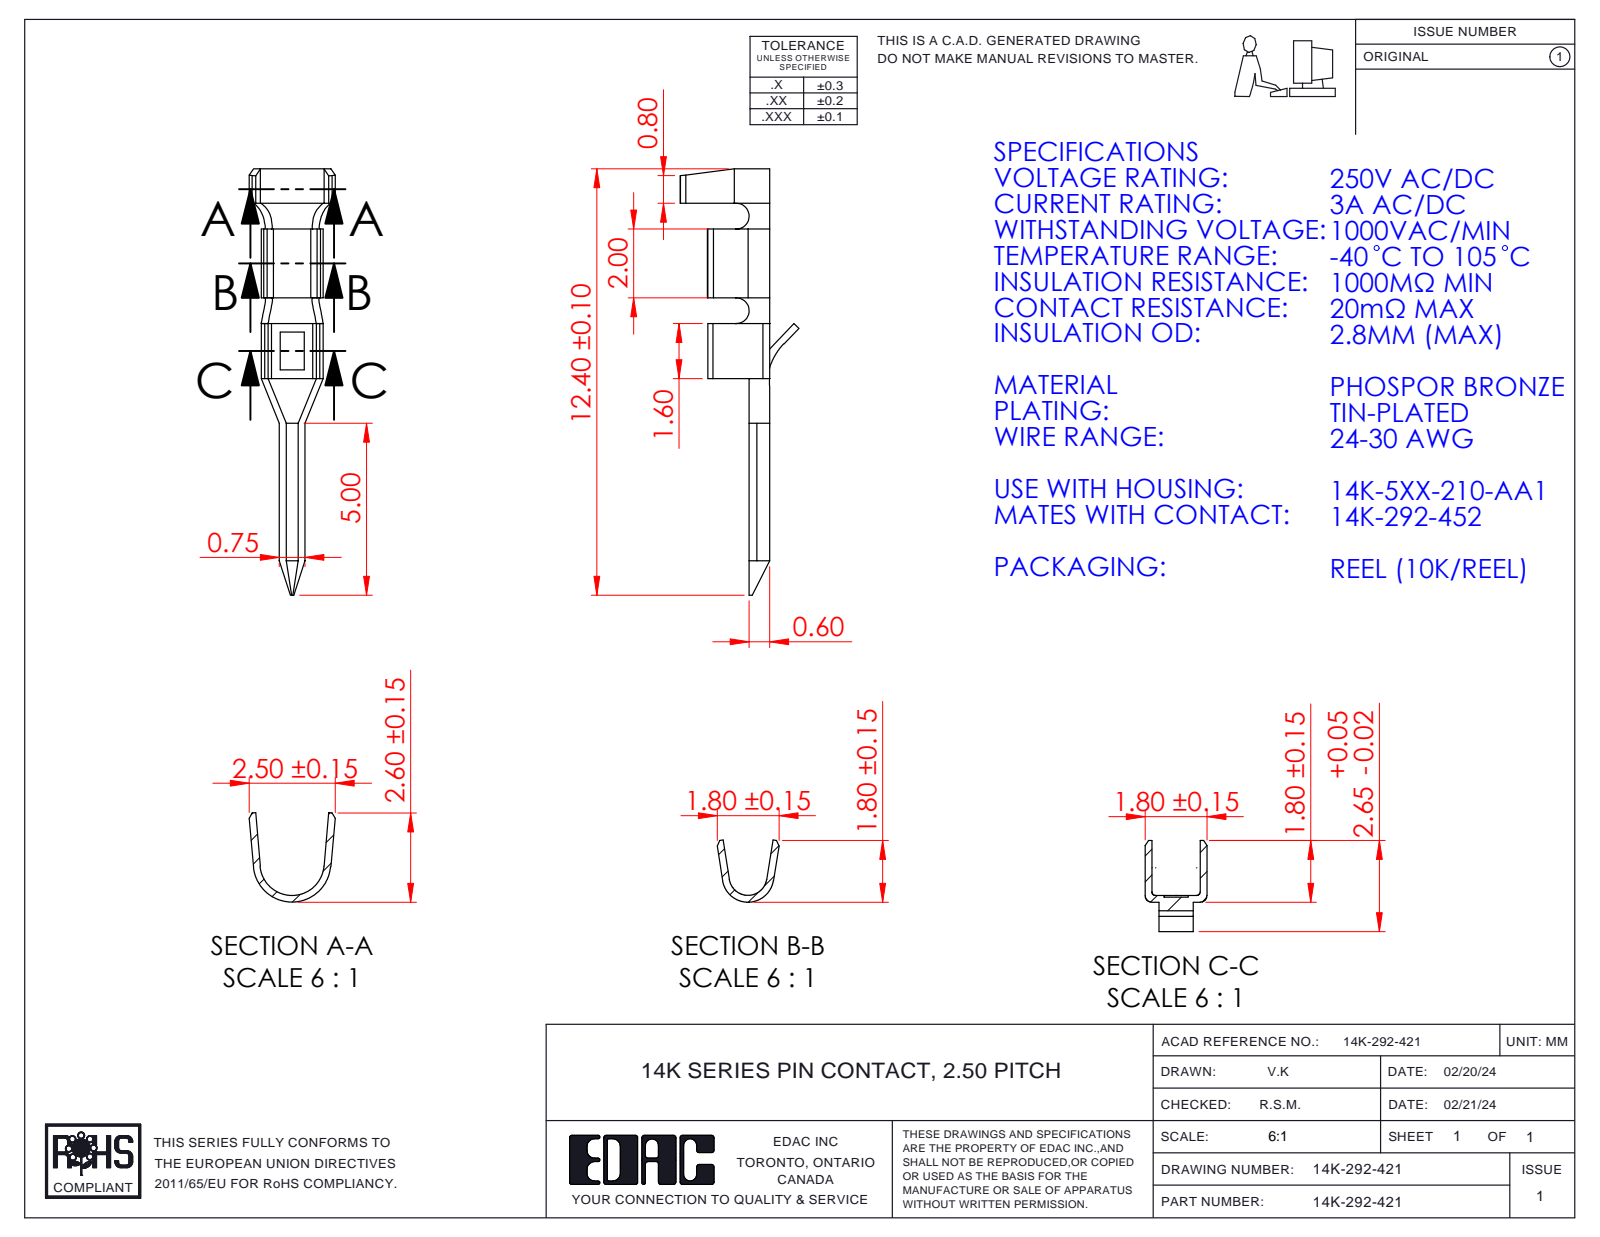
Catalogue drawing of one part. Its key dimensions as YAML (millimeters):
part_name: "14K-292-421"
step_written_by: "SolidWorks 2023 (CONFIG_CONTROL_DESIGN)"
units: millimeters
bodies: {solids: 1, faces: 97, planar: 60, cylindrical: 23, other: 14}
overall_size: [12.4, 3.46, 2.5]
volume: 7
surface_area: 78
partial_cylinders:
  - {radius: 0.38, count: 3}
  - {radius: 0.1, count: 2}
  - {radius: 0.2, count: 2}
  - {radius: 0.17, count: 1}
  - {radius: 0.55, count: 1}
  - {radius: 0.75, count: 1}
  - {radius: 0.93, count: 1}
  - {radius: 1.13, count: 1}
face_to_face_distances: [1.6, 1.4, 1.8, 0.73, 0.52, 0.55, 1.07, 0.53, 0.87, 1.28]
